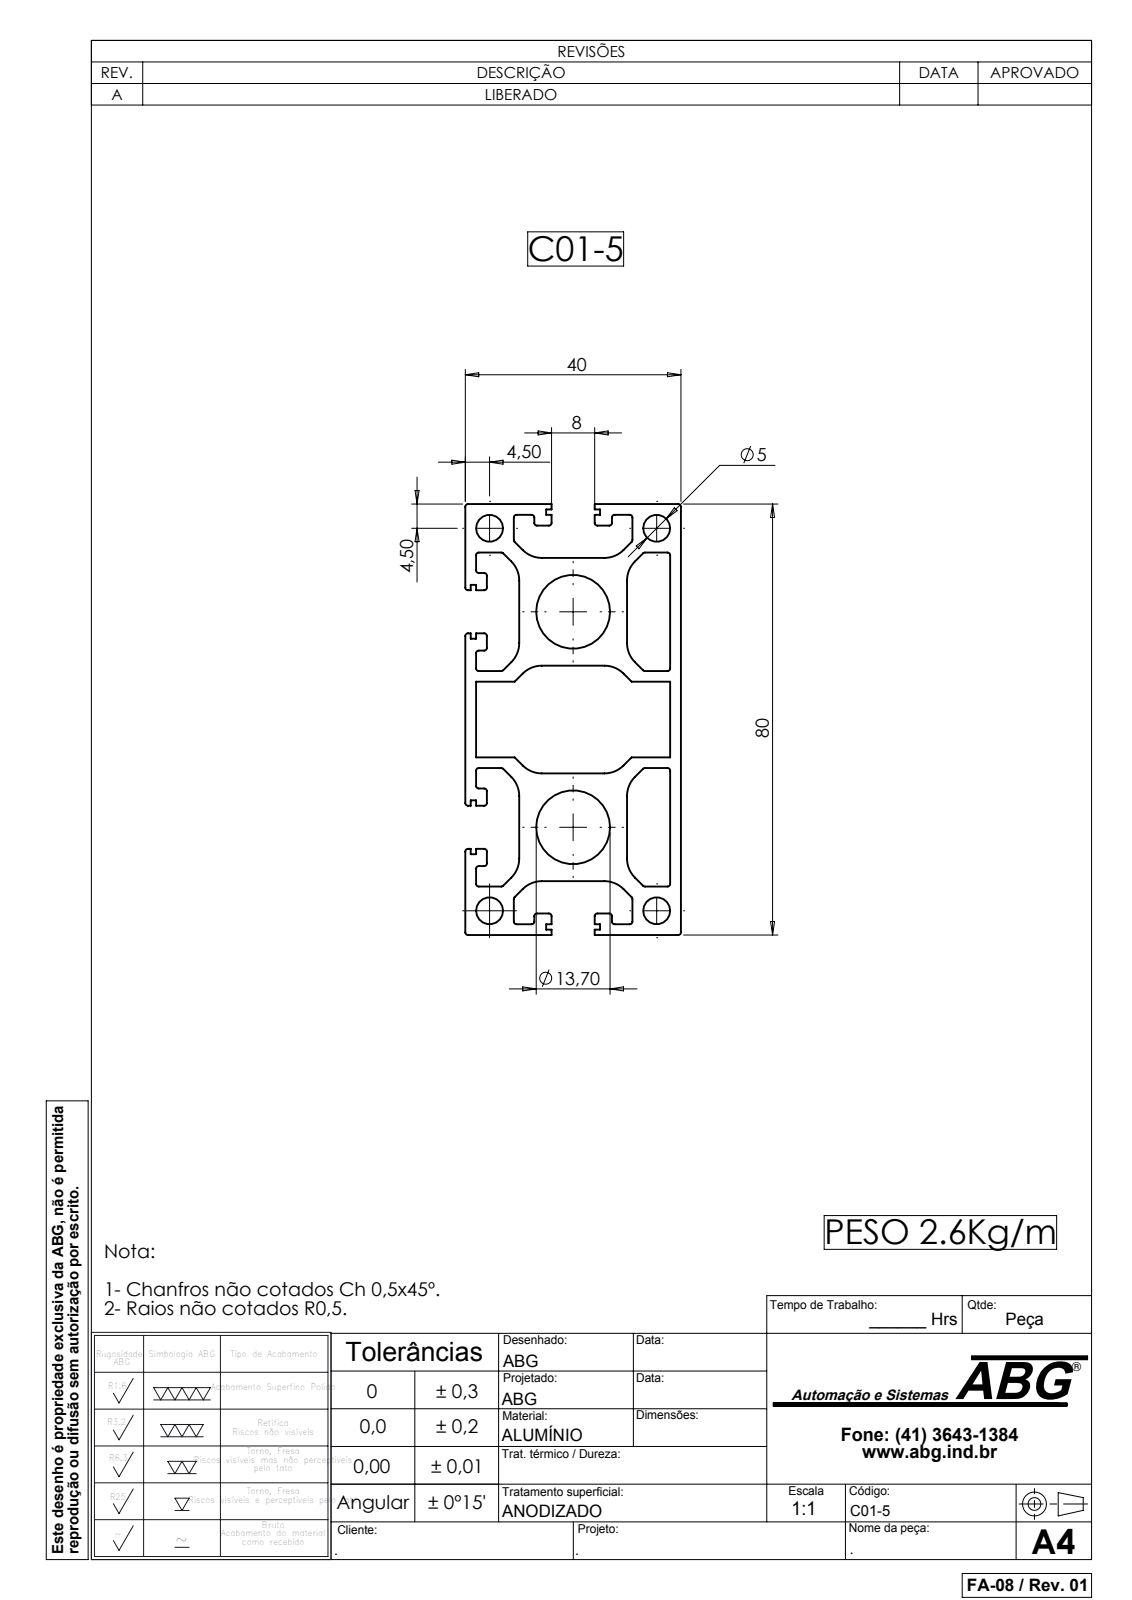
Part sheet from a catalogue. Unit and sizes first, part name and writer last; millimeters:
Units: millimetres
Overall size (bounding box): 6000 × 80 × 40
Round holes (diameter × count): ⌀5 ×4, ⌀13.7 ×2
Partial cylindrical surfaces — rounded edges, fillets, slot ends (radius × count): R0.5 ×56, R5 ×16
Main face-to-face distances: 2, 40, 38, 30, 8, 10, 1, 20, 28, 21
Hole centre spacings: 21.92, 57.62, 31, 71, 77.47, 40
Volume: 7 197 000 mm³ · Surface area: 4 916 000 mm²
Bodies: 1 solid, 202 faces (118 planar, 84 cylindrical, 0 other)
Part name (STEP PRODUCT): C01-5
STEP written by: SolidWorks 2007 (CONFIG_CONTROL_DESIGN)
